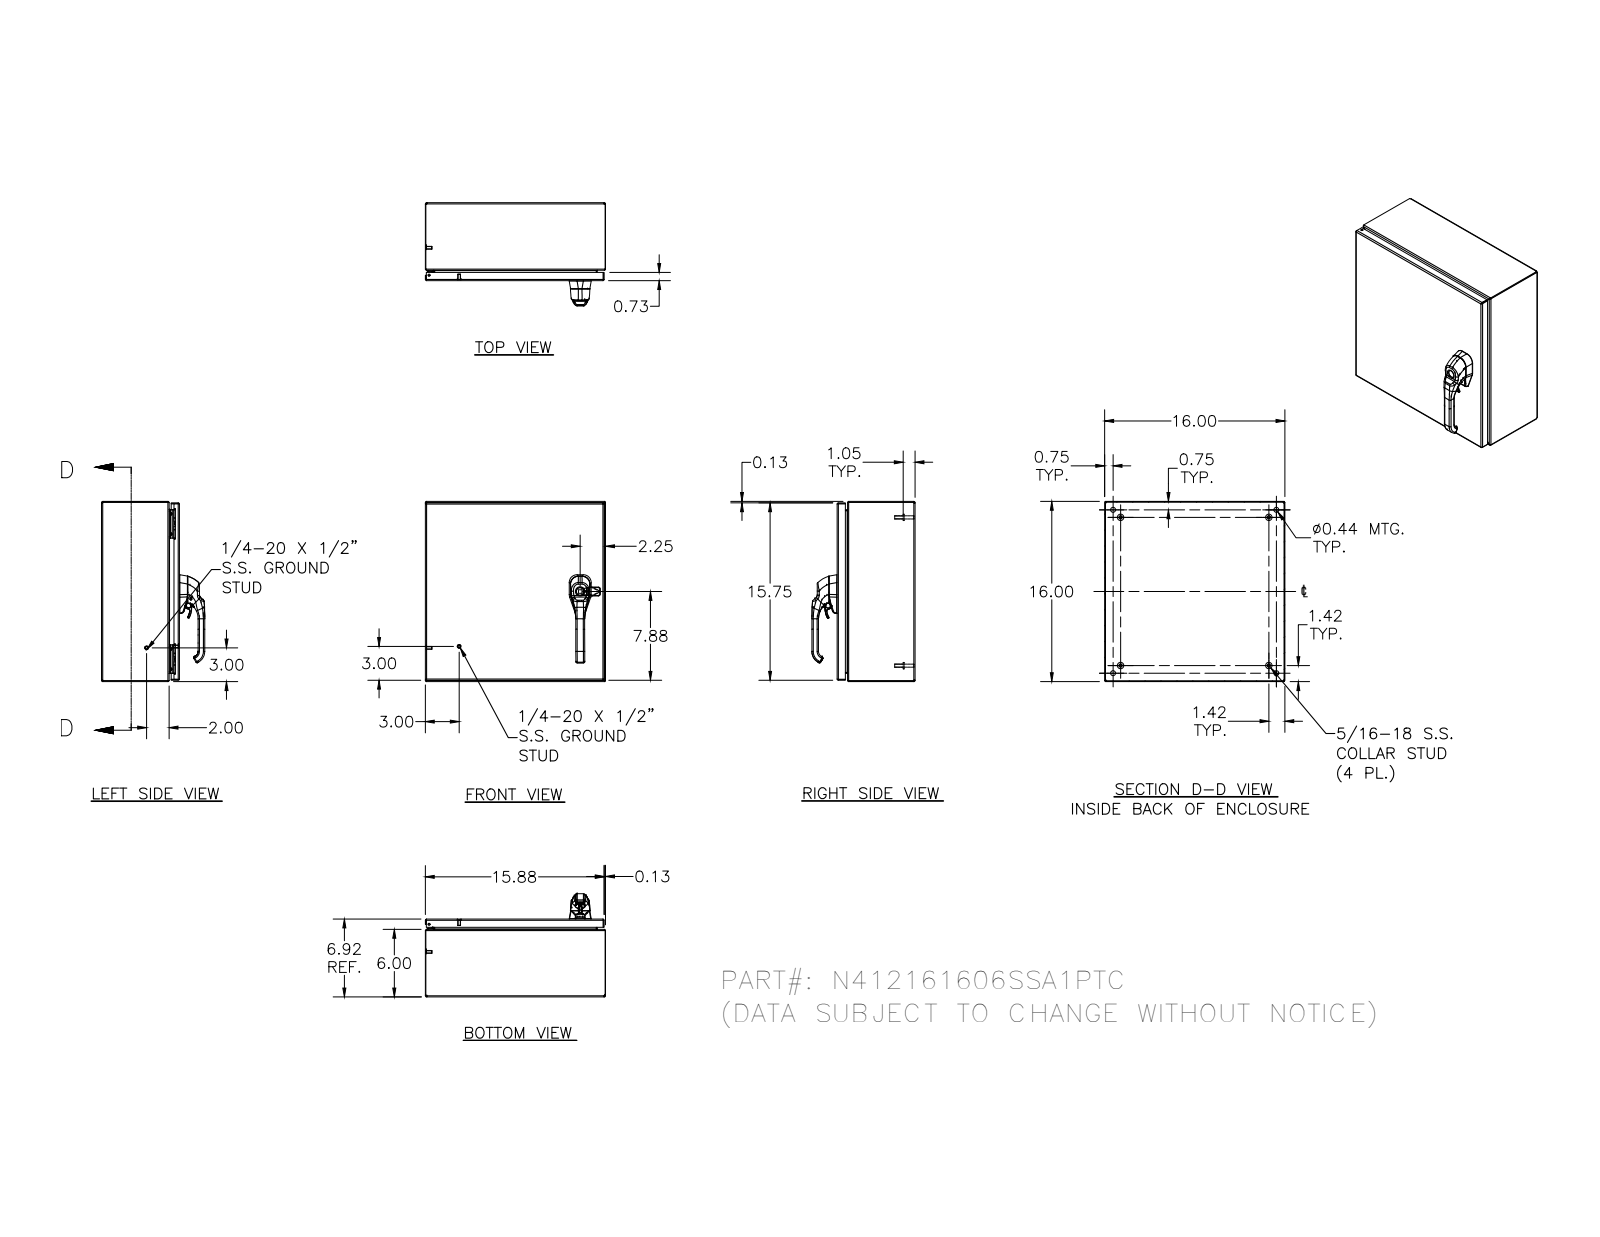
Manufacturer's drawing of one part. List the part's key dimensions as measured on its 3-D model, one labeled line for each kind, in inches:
Part name (STEP PRODUCT): N412161606SSA1PTC; N412161606SSA1PTCBKP; N4121616SSA1PTCLID; HFW328176 (+8 more)
STEP written by: Autodesk Inventor 2012 (AUTOMOTIVE_DESIGN)
Units: inches
Bodies: 41 solids, 2784 faces (882 planar, 1037 cylindrical, 865 other)
Overall size (bounding box): 16 × 16 × 9.166
Volume: 83.3 in³ · Surface area: 2 168 in²
Round holes (diameter × count): ⌀0.188 ×5, ⌀0.093 ×4, ⌀0.152 ×4, ⌀0.167 ×4, ⌀0.172 ×4, ⌀0.437 ×4, ⌀0.213 ×3, ⌀0.281 ×3, ⌀0.156 ×2, ⌀0.315 ×2, ⌀0.402 ×2, ⌀0.413 ×2
Round bosses / shafts (diameter × count): ⌀0.25 ×10, ⌀0.563 ×4, ⌀0.36 ×4, ⌀0.32 ×4, ⌀0.3 ×4, ⌀0.275 ×4, ⌀0.256 ×4, ⌀0.164 ×4
Partial cylindrical surfaces — rounded edges, fillets, slot ends (radius × count): R0.02 ×173, R0.012 ×101, R0.031 ×30, R0.05 ×26, R0.019 ×21, R0.105 ×20, R0.016 ×18, R0.079 ×14
Main face-to-face distances: 0.074, 6.843, 15.926, 6.917, 6.769, 16, 15.852, 5.926, 0.917, 0.125
Hole centre spacings: 11.996, 14.5, 0.017, 0.66, 12.656, 14.181, 15.173, 0.019
